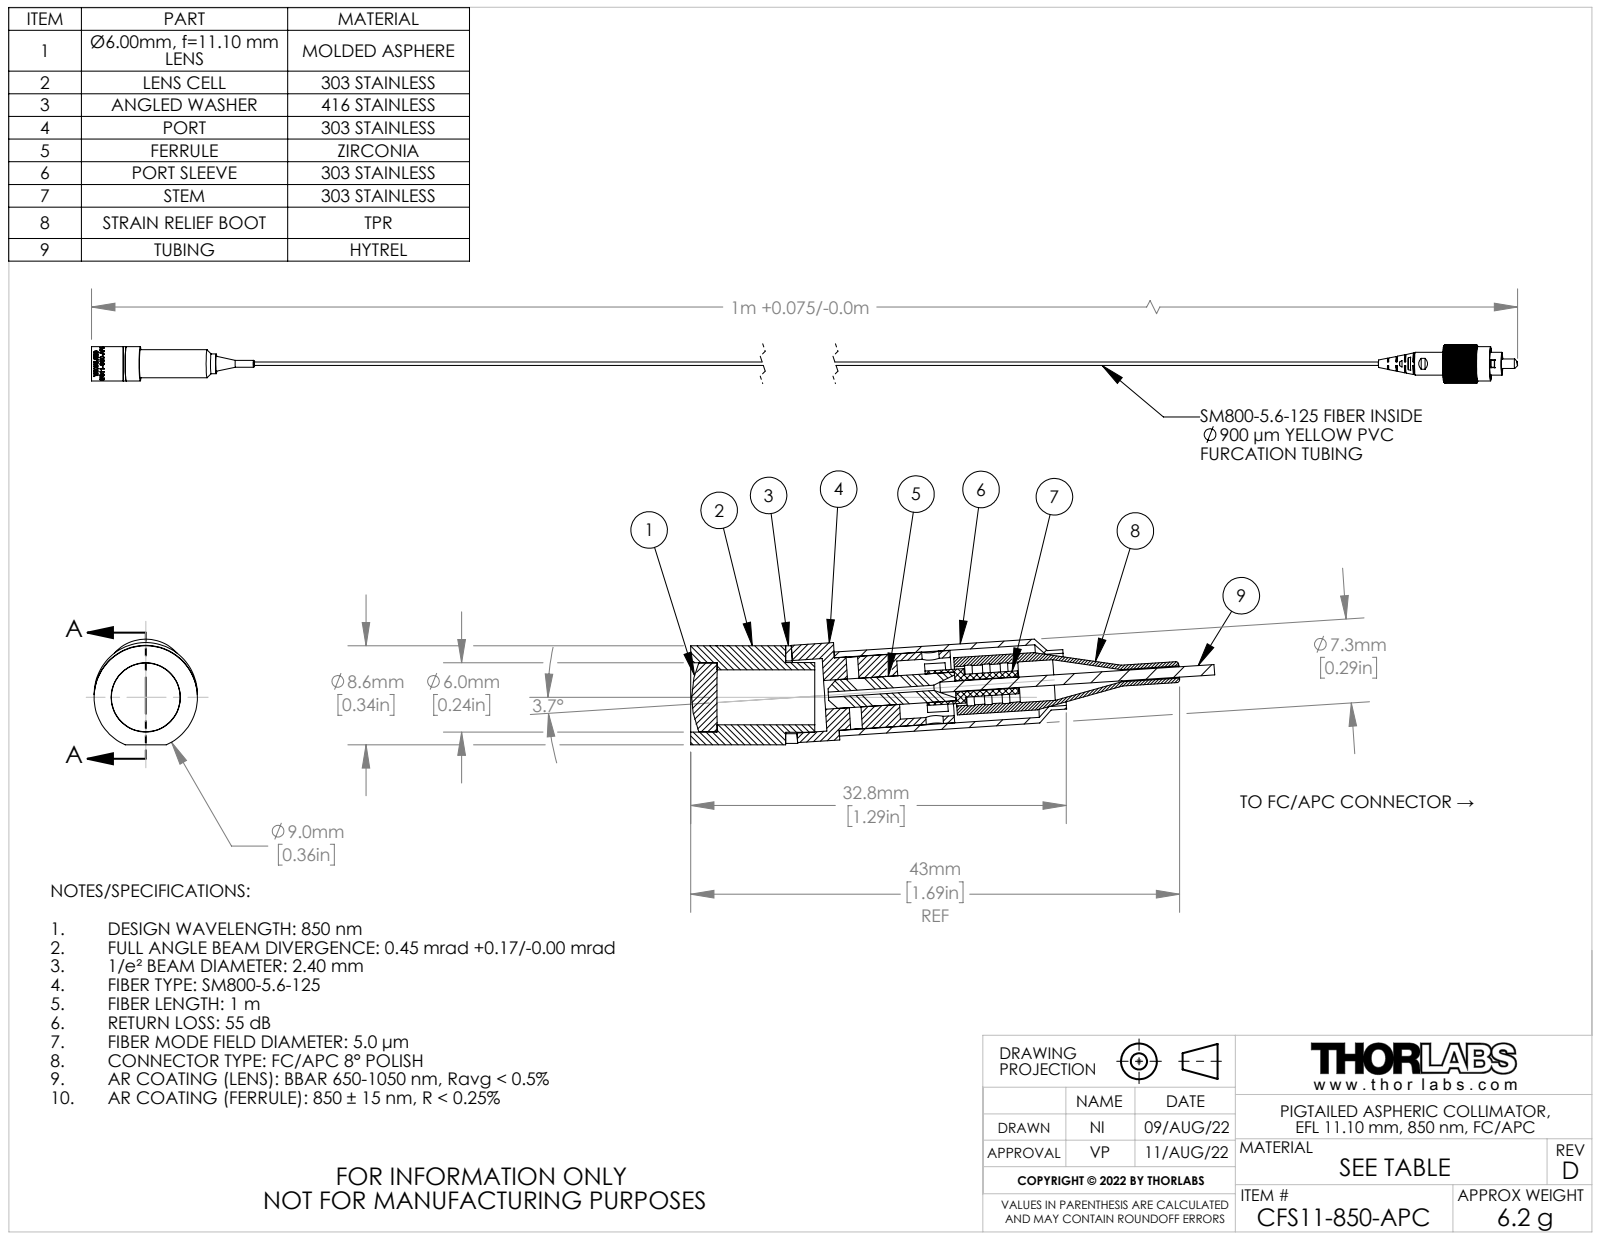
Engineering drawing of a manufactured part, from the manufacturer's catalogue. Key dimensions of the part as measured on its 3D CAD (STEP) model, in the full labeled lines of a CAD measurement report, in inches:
Part name (STEP PRODUCT): 19173-E0W
STEP written by: SolidWorks 2018 (CONFIG_CONTROL_DESIGN)
Units: inches
Bodies: 12 solids, 521 faces (252 planar, 223 cylindrical, 46 other)
Overall size (bounding box): 40.592 × 2.936 × 0.393
Volume: 0.158 in³ · Surface area: 12.2 in²
Round holes (diameter × count): ⌀0.04 ×2, ⌀0.059 ×2, ⌀0.2 ×2, ⌀0.25 ×2, ⌀0.018 ×1, ⌀0.039 ×1, ⌀0.042 ×1, ⌀0.055 ×1, ⌀0.098 ×1, ⌀0.098 ×1, ⌀0.119 ×1, ⌀0.12 ×1
Round bosses / shafts (diameter × count): ⌀0.355 ×1, ⌀0.354 ×1, ⌀0.289 ×1, ⌀0.28 ×1, ⌀0.249 ×1, ⌀0.24 ×1, ⌀0.236 ×1, ⌀0.235 ×1
Partial cylindrical surfaces — rounded edges, fillets, slot ends (radius × count): R0.089 ×1, R0.117 ×1, R0.197 ×1
Main face-to-face distances: 0.267, 0.267, 39.72, 39.658, 0.062, 0.145, 39.513, 39.575, 0.326, 39.76
Hole centre spacings: 0.02, 0.02, 0.27, 0.27
